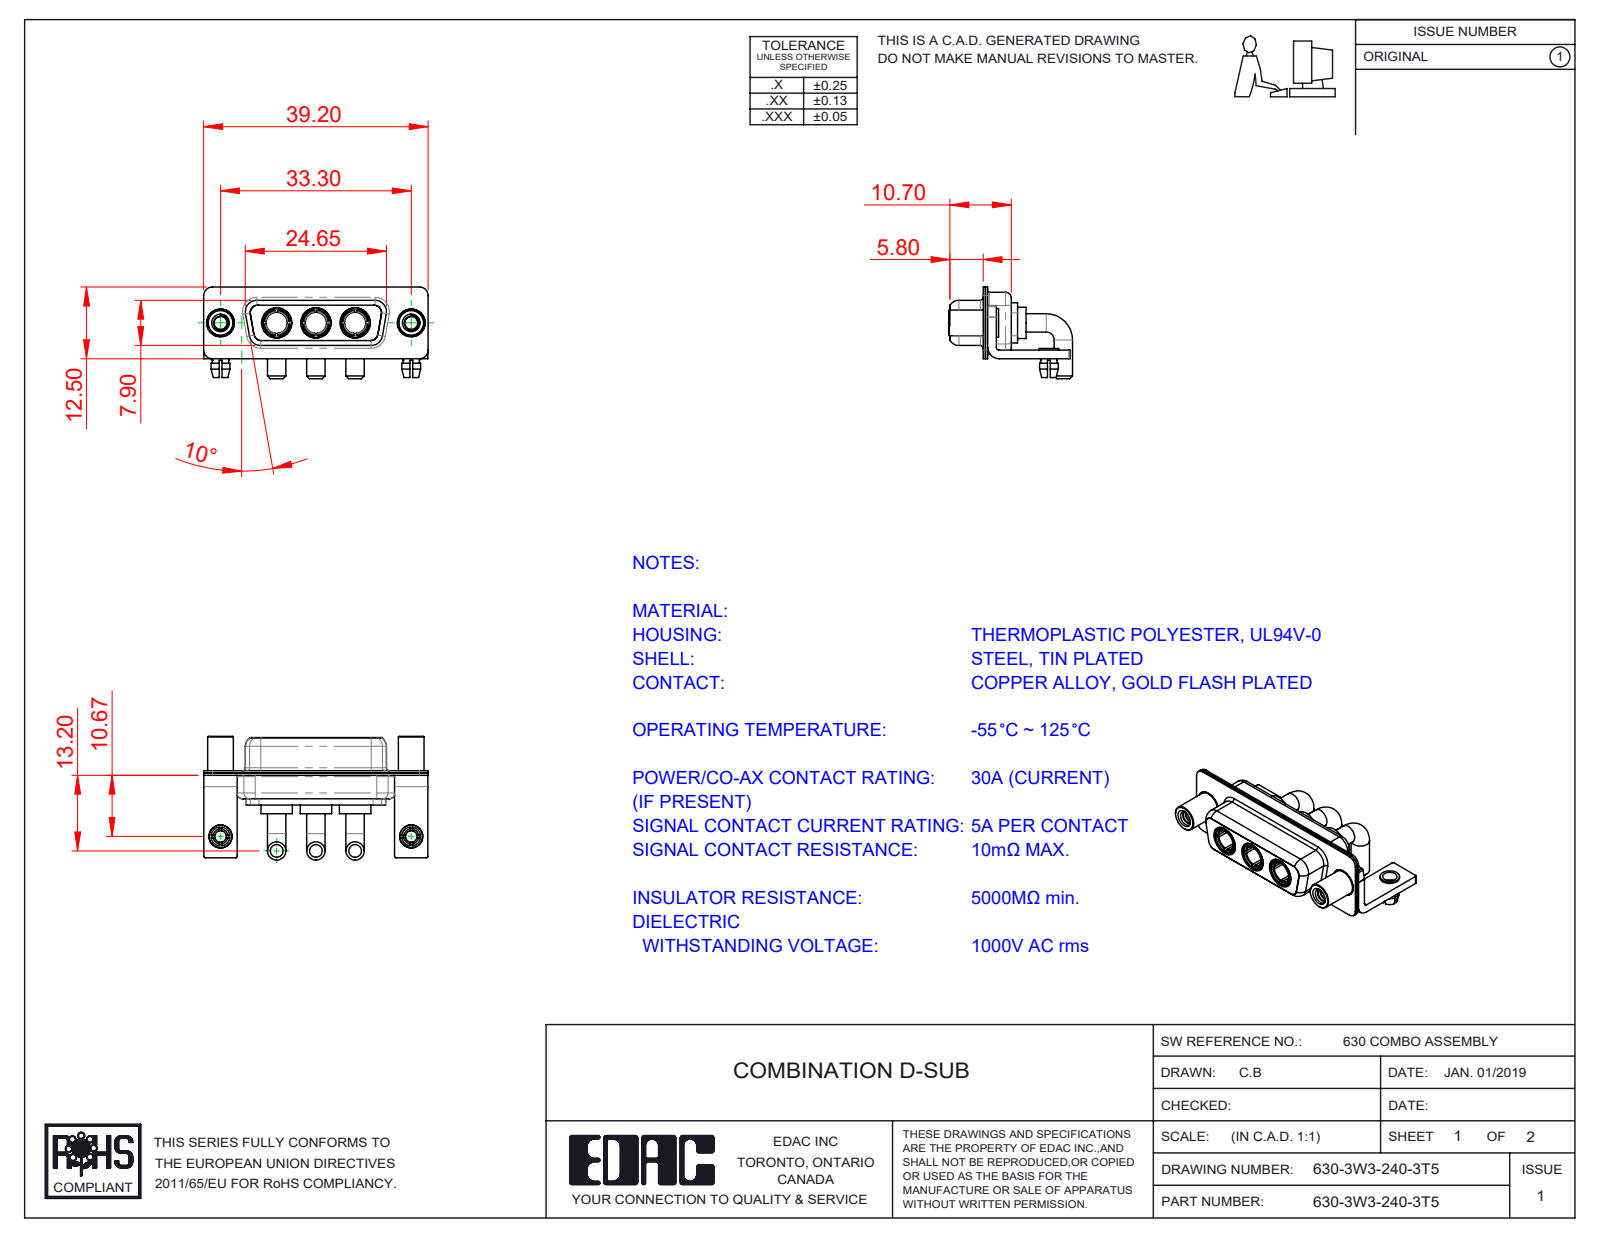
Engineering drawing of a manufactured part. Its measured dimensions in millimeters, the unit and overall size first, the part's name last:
Units: millimetres
Overall size (bounding box): 39.2 × 21.6 × 16
Round holes (diameter × count): ⌀4.85 ×5, ⌀3.7 ×3, ⌀5.3 ×3, ⌀2 ×2, ⌀2.26 ×2, ⌀2.5 ×2, ⌀3.2 ×2, ⌀4 ×2, ⌀4.05 ×2
Round bosses / shafts (diameter × count): ⌀3.2 ×6, ⌀5.5 ×3, ⌀5.2 ×3, ⌀4.96 ×3, ⌀4.75 ×3, ⌀3.75 ×3, ⌀5 ×2, ⌀4.95 ×2
Partial cylindrical surfaces — rounded edges, fillets, slot ends (radius × count): R0.25 ×16, R1.5 ×16, R2 ×13, R1.35 ×12, R1.6 ×8, R0.5 ×5, R0.6 ×4, R0.65 ×4
Main face-to-face distances: 0.4, 0.8, 1.4, 0.45, 1.5, 8.45, 1.8, 8.9, 7.05, 5.2
Hole centre spacings: 6.85, 9.8, 16.65, 23.5, 33.3, 13.7
Volume: 3 159 mm³ · Surface area: 7 105 mm²
Bodies: 15 solids, 693 faces (224 planar, 304 cylindrical, 165 other)
Part name (STEP PRODUCT): 630Combo Stabilizer Bracket; 630Combo Shell Rear_15 Contacts; 630Combo Board Lock; 630Combo Housing_3W3 (+4 more)
STEP written by: SolidWorks 2020 (CONFIG_CONTROL_DESIGN)
